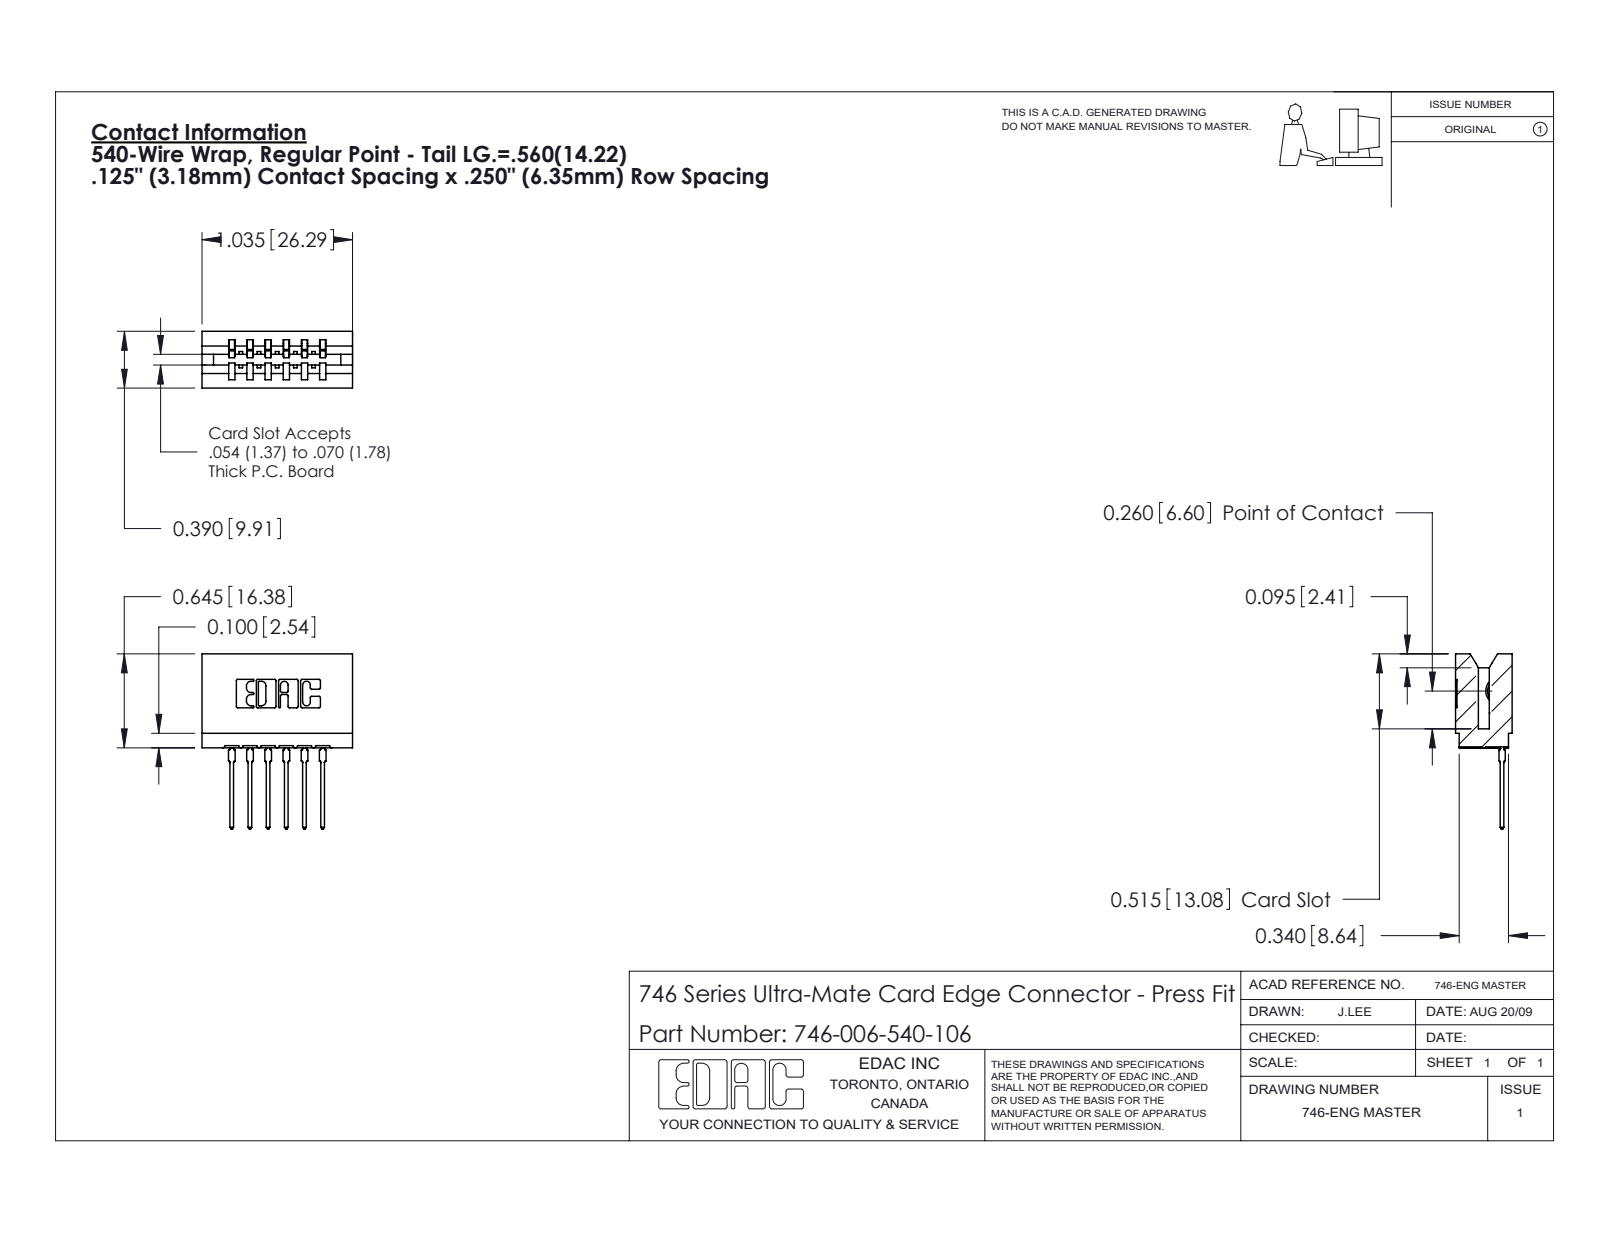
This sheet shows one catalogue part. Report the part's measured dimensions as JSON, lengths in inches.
{"part_name": "746-292-001_540; 746-006-540-106; 746 Part_.515 Slot Depth - 06", "step_written_by": "SolidWorks 2020 (CONFIG_CONTROL_DESIGN)", "units": "inches", "bodies": {"solids": 7, "faces": 746, "planar": 434, "cylindrical": 156, "other": 156}, "overall_size": [1.204, 1.035, 0.39], "volume_in3": 0.182, "surface_area_in2": 6.051, "partial_cylinders_radius": [[0.01, 22], [0.021, 12], [0.015, 7], [0.007, 6], [0.031, 6], [0.005, 4], [0.011, 4], [0.026, 3]], "face_to_face_distances": [0.25, 0.125, 0.042, 0.333, 0.057, 0.39, 0.292, 0.5, 0.208, 0.125]}
